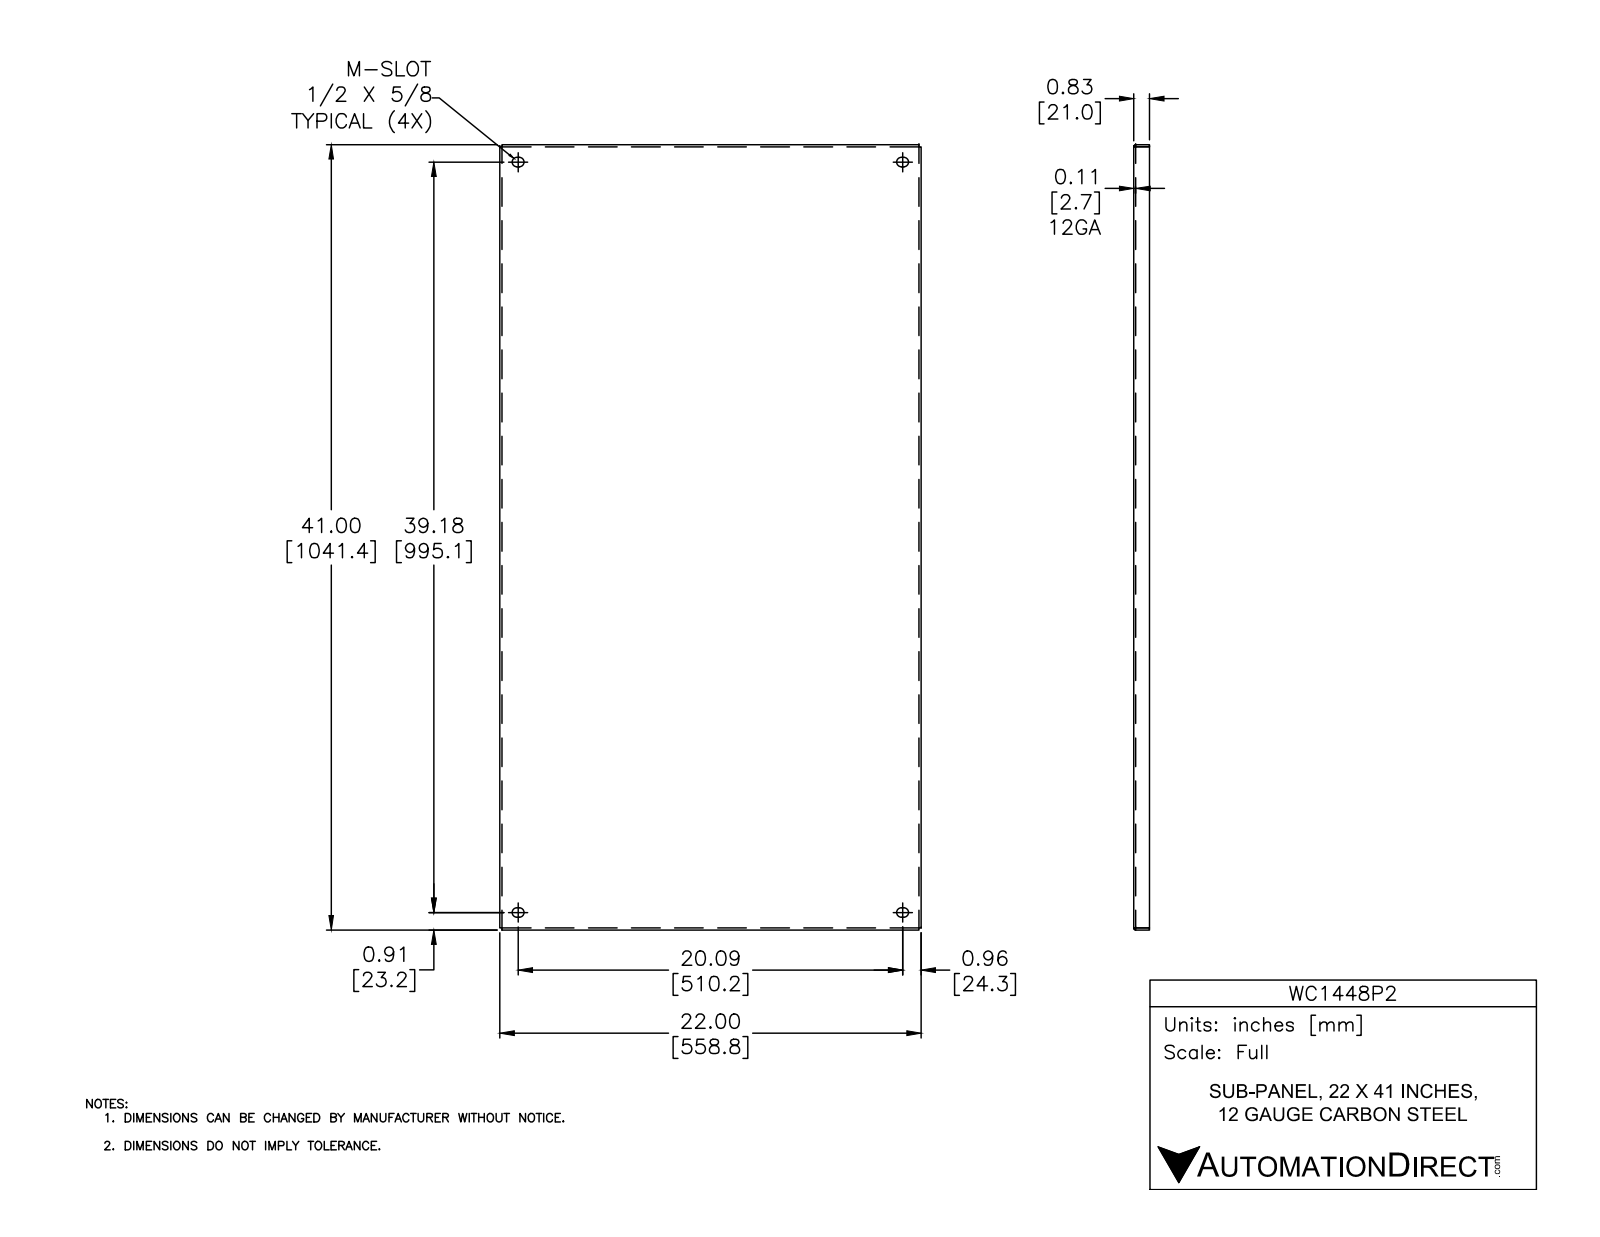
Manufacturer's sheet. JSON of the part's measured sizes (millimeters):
{"part_name": "WC1448P2", "step_written_by": "SolidWorks 2014 (AUTOMOTIVE_DESIGN)", "units": "millimeters", "bodies": {"solids": 1, "faces": 58, "planar": 30, "cylindrical": 20, "other": 8}, "overall_size": [1043, 738.2, 21], "volume_mm3": 2211000, "surface_area_mm2": 1675000, "partial_cylinders_radius": [[6.4, 8], [2.7, 3], [2.7, 1]], "face_to_face_distances": [2.7, 735.5, 1040.3, 738.2, 732.9, 1043, 1037.7, 21, 18.4, 2.8]}
